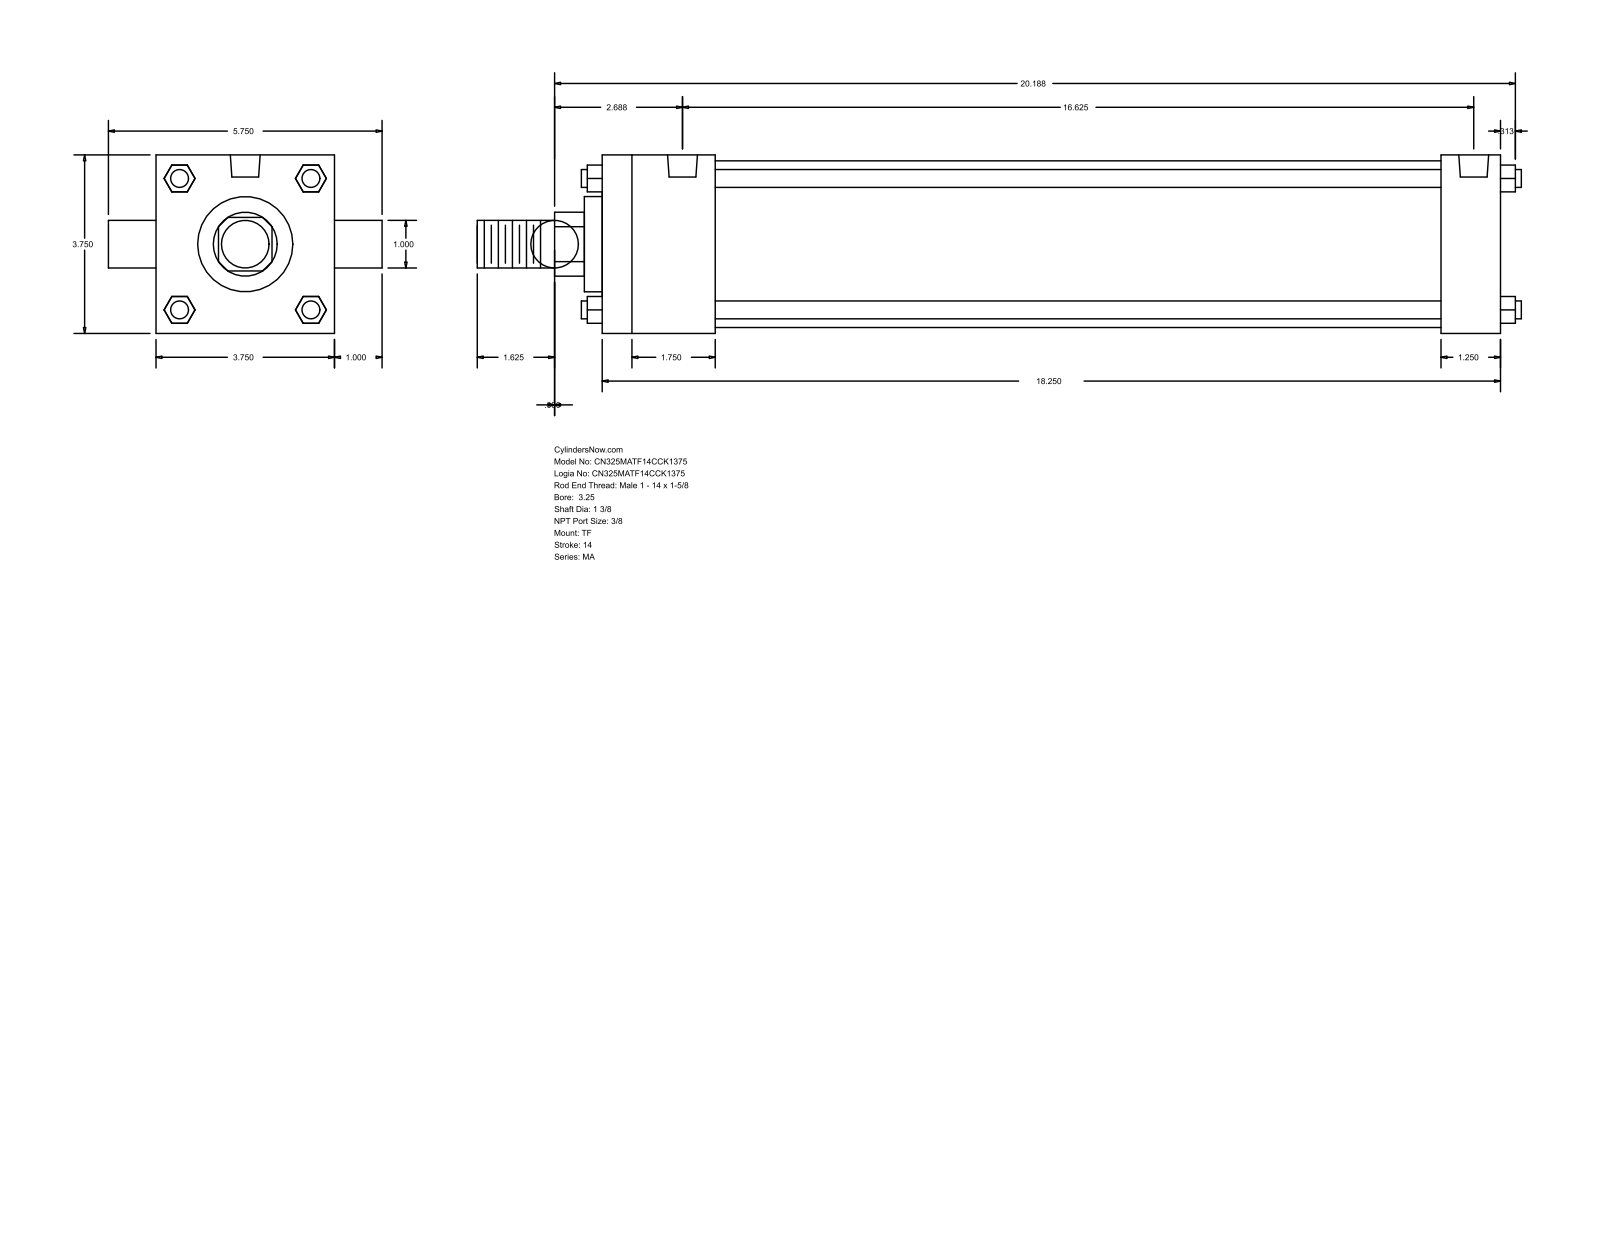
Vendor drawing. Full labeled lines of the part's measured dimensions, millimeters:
Part name (STEP PRODUCT): MA_TF__0325_1.375
STEP written by: GSSL Pune (CONFIG_CONTROL_DESIGN)
Units: millimetres
Bodies: 0 solids, 120 faces (92 planar, 28 cylindrical, 0 other)
Overall size (bounding box): 557.21 × 146.05 × 95.25
Round holes (diameter × count): ⌀11.11 ×3, ⌀15.93 ×2
Round bosses / shafts (diameter × count): ⌀9.53 ×4, ⌀25.4 ×2, ⌀88.9 ×1, ⌀50.8 ×1, ⌀34.92 ×1
Partial cylindrical surfaces — rounded edges, fillets, slot ends (radius × count): R17.06 ×1
Main face-to-face distances: 95.24, 479.42, 60.32, 447.67, 387.35, 419.1, 31.75, 9.52, 69.84, 457.19
Hole centre spacings: 4.77, 417.51, 412.74, 422.28
